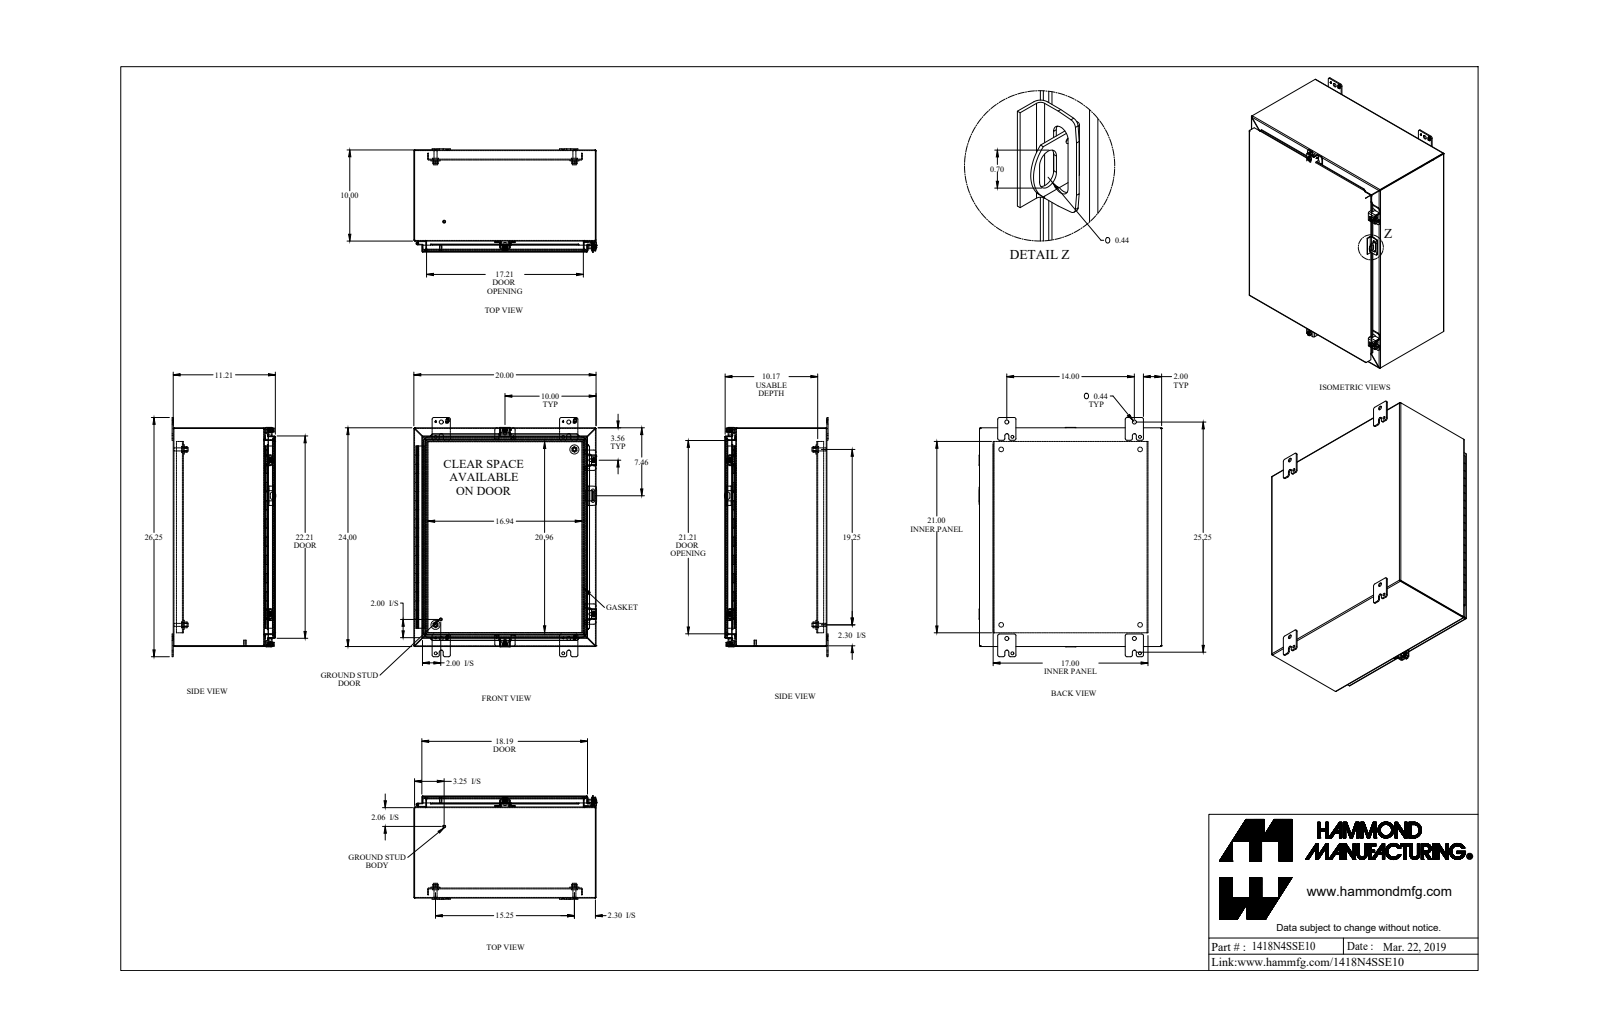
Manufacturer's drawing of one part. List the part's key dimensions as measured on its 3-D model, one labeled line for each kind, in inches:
Part name (STEP PRODUCT): 1418N4SSE10_Default
STEP written by: SolidWorks 2019 (CONFIG_CONTROL_DESIGN)
Units: inches
Bodies: 39 solids, 1499 faces (925 planar, 481 cylindrical, 93 other)
Overall size (bounding box): 26.25 × 20.063 × 11.375
Volume: 197.4 in³ · Surface area: 5 221 in²
Round holes (diameter × count): ⌀0.213 ×4, ⌀0.313 ×4, ⌀0.375 ×4, ⌀0.437 ×4, ⌀0.5 ×4, ⌀0.265 ×2, ⌀0.265 ×2, ⌀0.307 ×2, ⌀0.445 ×2, ⌀0.125 ×1, ⌀0.187 ×1
Round bosses / shafts (diameter × count): ⌀0.65 ×4, ⌀0.5 ×4, ⌀0.39 ×4, ⌀0.375 ×4, ⌀0.332 ×4, ⌀0.244 ×4, ⌀1 ×2, ⌀0.313 ×2
Partial cylindrical surfaces — rounded edges, fillets, slot ends (radius × count): R0.188 ×26, R0.036 ×24, R0.108 ×24, R0.048 ×21, R0.143 ×21, R0.25 ×20, R0.125 ×10, R0.045 ×8
Main face-to-face distances: 0.072, 19.928, 11.066, 11.138, 0.072, 11.138, 11.21, 23.928, 0.095, 0.937
Hole centre spacings: 7.916, 22.694, 14, 24.559, 1.735, 2.434, 14.702, 15.25
